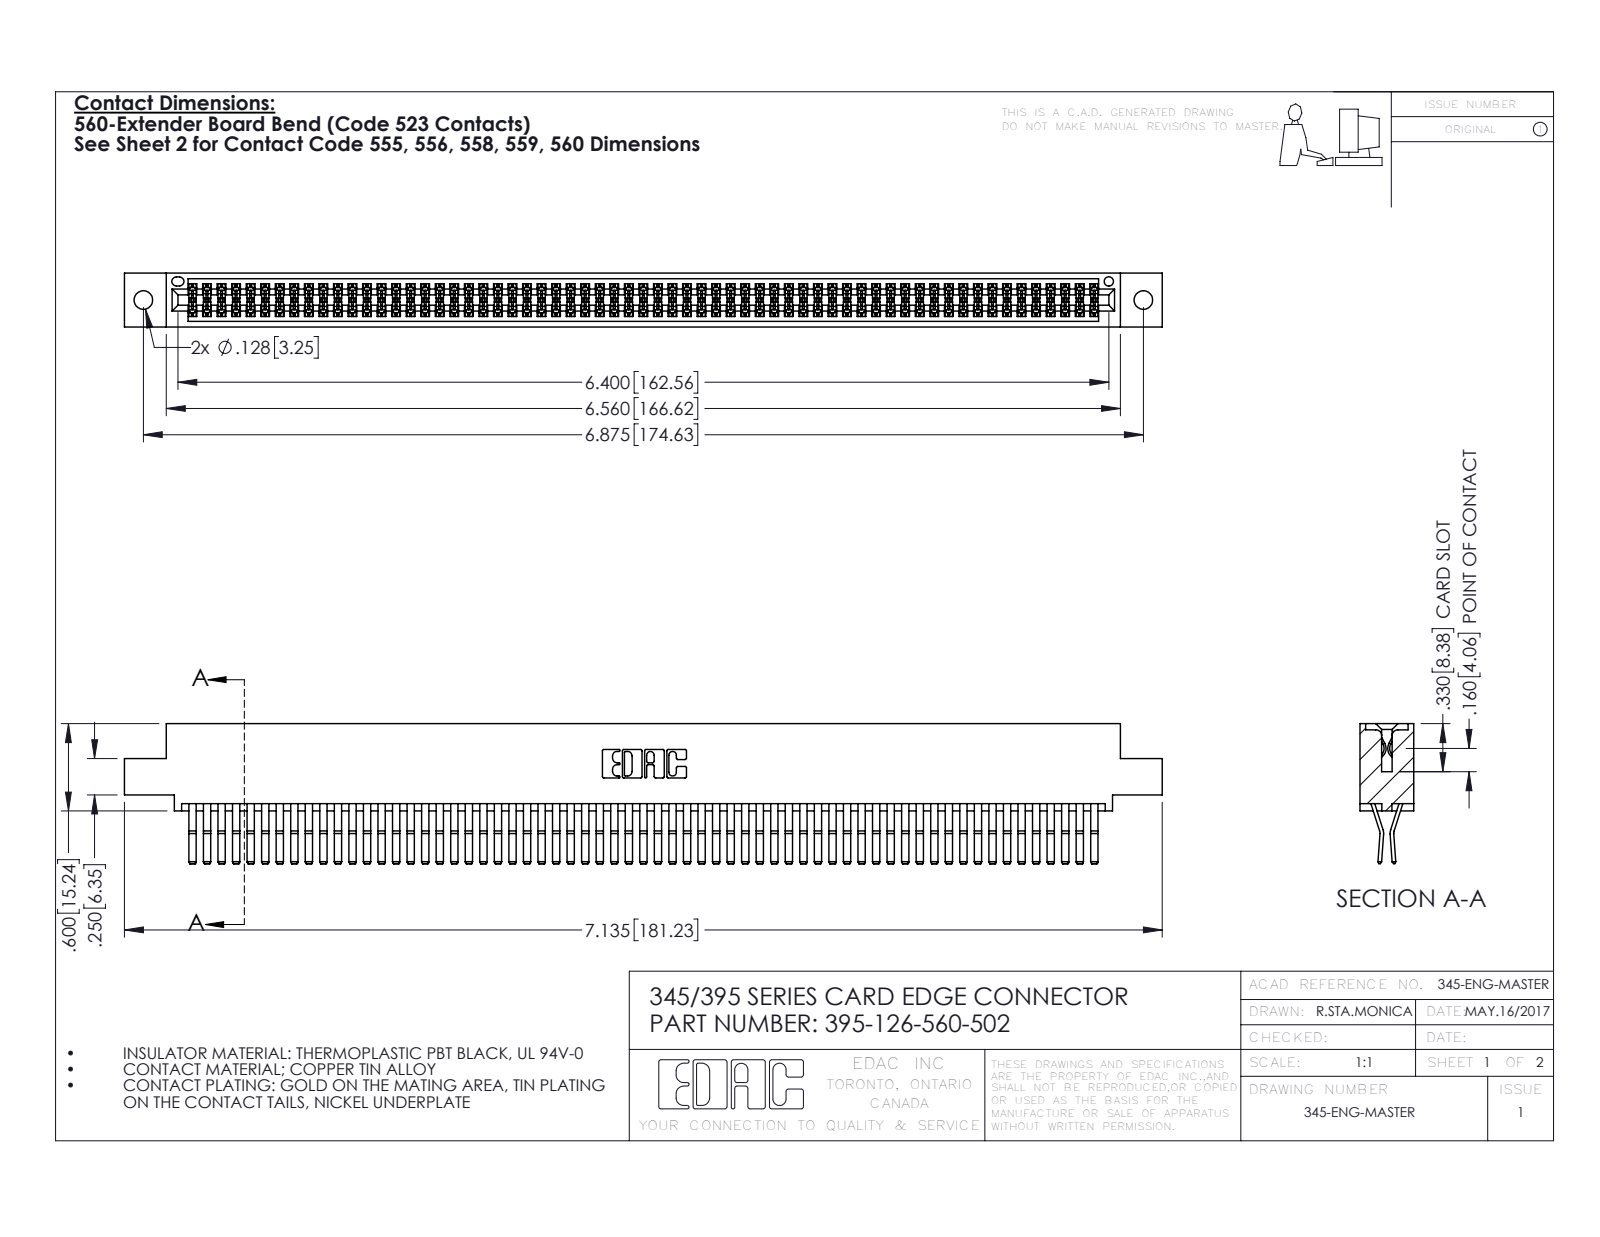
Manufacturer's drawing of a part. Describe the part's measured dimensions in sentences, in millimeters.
The part is named "345 Part_0.110 Offset - 0.128 Dia; 395-126-560-502; 345-292-001_560 Tail". Its 3-D file was written by "SolidWorks 2016 (CONFIG_CONTROL_DESIGN)". It is 127 solids with 6682 faces: 4242 planar, 2440 cylindrical and 0 other. Overall it measures 181.2 by 24.4 by 9.4 millimeters. Its volume is 18 520 cubic millimeters and its surface area 29 720 square millimeters. Round holes: 2 of diameter 3.3, 1 of diameter 1.6. Partial cylindrical surfaces (rounded edges, fillets, slot ends): 190 of radius 0.2, 22 of radius 0.3, 6 of radius 0.2, 6 of radius 0.8, 3 of radius 0.7, 2 of radius 0.3, 2 of radius 0.4, 2 of radius 0.5. The main face-to-face distances are 0.6, 7.6, 1.8, 9.4, 5.1, 2.5, 6.9, 5.7, 4.4, 3.8. The hole center spacings are 6.9, 168.6, 174.6.
